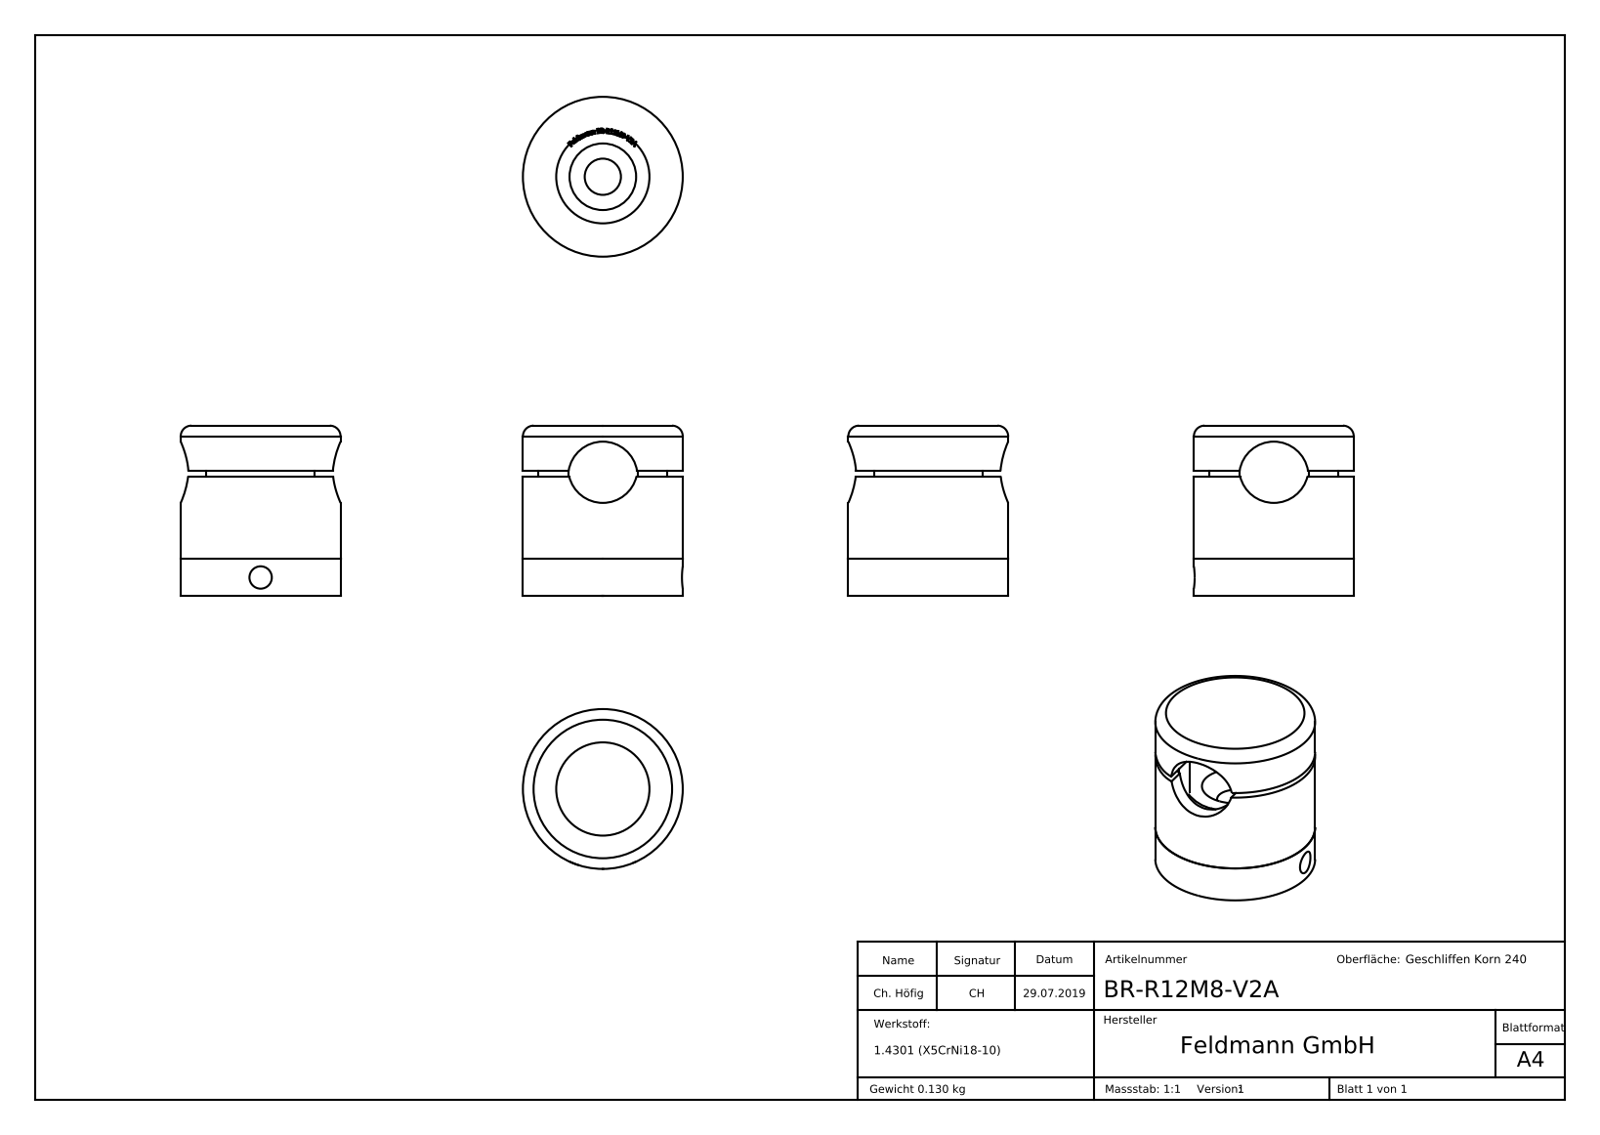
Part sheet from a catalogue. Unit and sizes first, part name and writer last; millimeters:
Units: millimetres
Overall size (bounding box): 64.34 × 30 × 30
Round holes (diameter × count): ⌀4.2 ×1, ⌀6.8 ×1, ⌀12.5 ×1, ⌀24.2 ×1
Round bosses / shafts (diameter × count): ⌀30 ×1, ⌀20 ×1
Partial cylindrical surfaces — rounded edges, fillets, slot ends (radius × count): R6.5 ×2, R8.75 ×1, R12.05 ×1
Main face-to-face distances: 7, 32, 25, 16, 8.5, 7.5, 23.5, 16.5, 22.5, 15.5
Volume: 16 514 mm³ · Surface area: 9 558 mm²
Bodies: 3 solids, 322 faces (185 planar, 15 cylindrical, 122 other)
Part name (STEP PRODUCT): BR-R12M8-V2A; BR-R1XM8-XXX Teil3_BR-R12M8-V2A Teil3; BR-R1XM8-XXX Teil1_BR-1XM8-V2A Teil1; BR-R1XM8-XXX Teil2_BR-R12M8-V2A Teil2 (+3 more)
STEP written by: SolidWorks 2015 (CONFIG_CONTROL_DESIGN)
